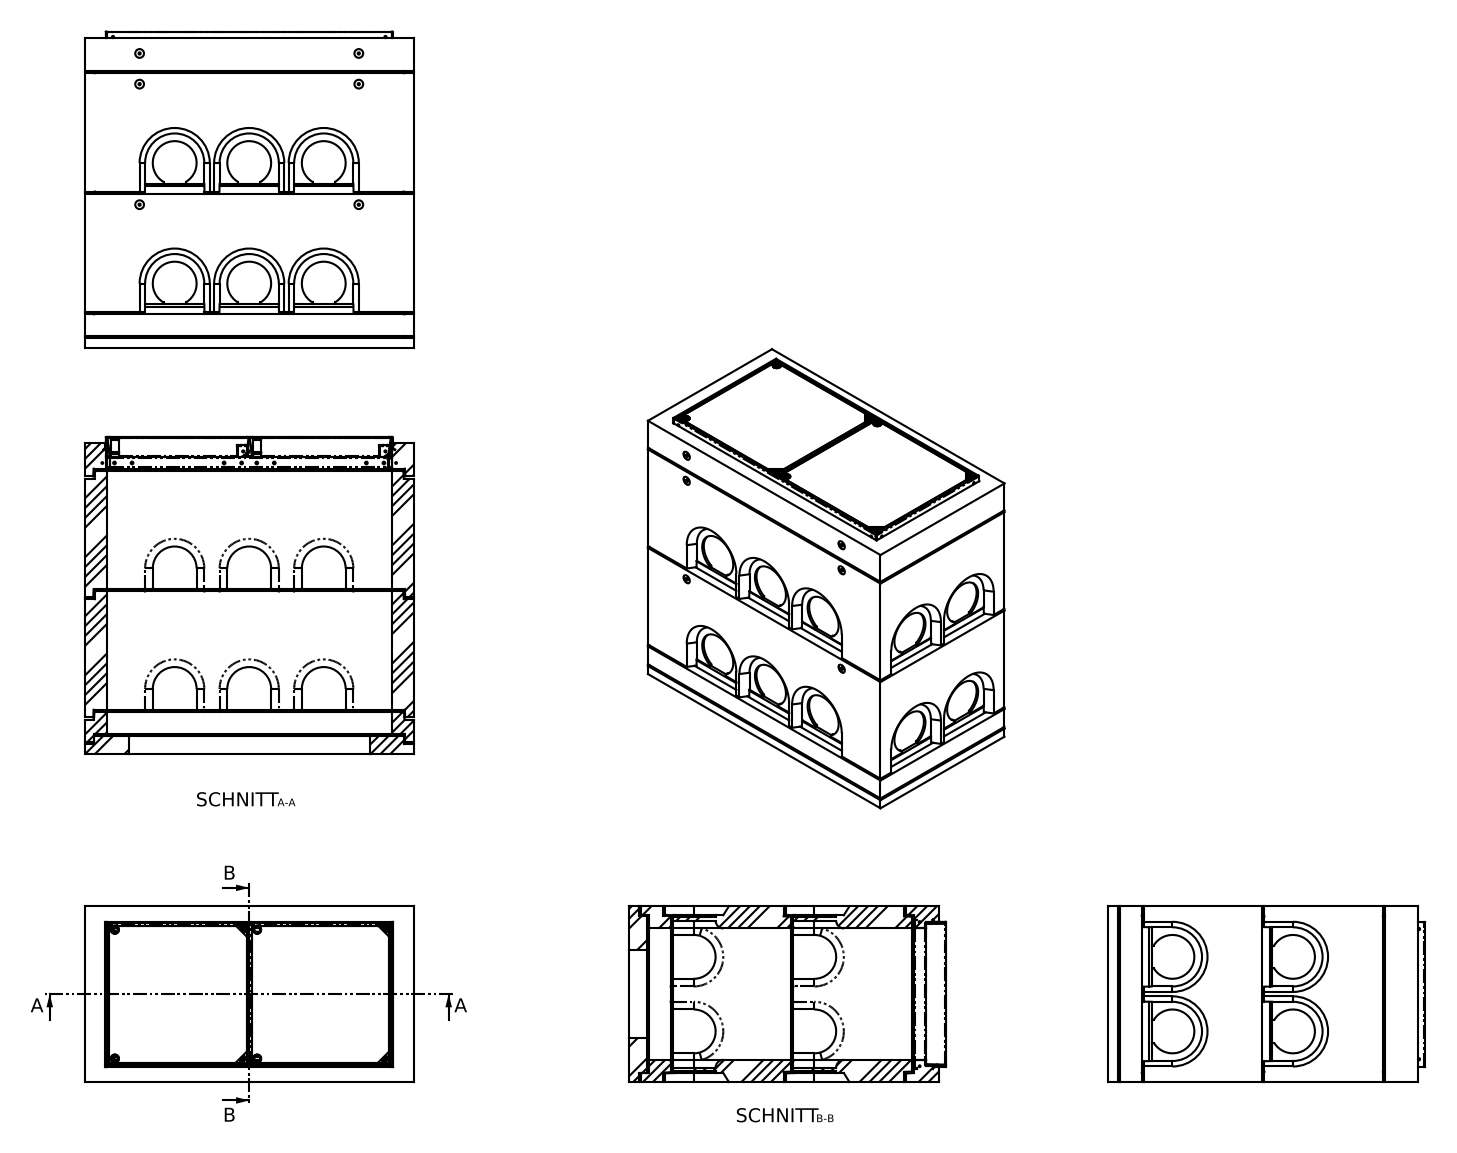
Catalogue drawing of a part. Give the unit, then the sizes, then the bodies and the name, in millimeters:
Units: millimetres
Overall size (bounding box): 1500 × 1445 × 800
Round holes (diameter × count): ⌀200 ×10, ⌀40 ×6, ⌀26.5 ×4, ⌀35 ×4, ⌀10 ×2
Round bosses / shafts (diameter × count): ⌀10 ×6, ⌀5.81 ×6
Partial cylindrical surfaces — rounded edges, fillets, slot ends (radius × count): R35 ×20, R3 ×8, R2.5 ×6, R13.5 ×4
Main face-to-face distances: 100, 700, 800, 10, 50, 35, 550, 25, 600, 1500
Hole centre spacings: 550, 340, 646.61, 393.95, 616.12, 913.89, 1000, 140
Bodies: 0 solids, 486 faces (300 planar, 116 cylindrical, 70 other)
Part name (STEP PRODUCT): SC-ECO.0613.138.125
STEP written by: SolidWorks 2018 (AUTOMOTIVE_DESIGN)
